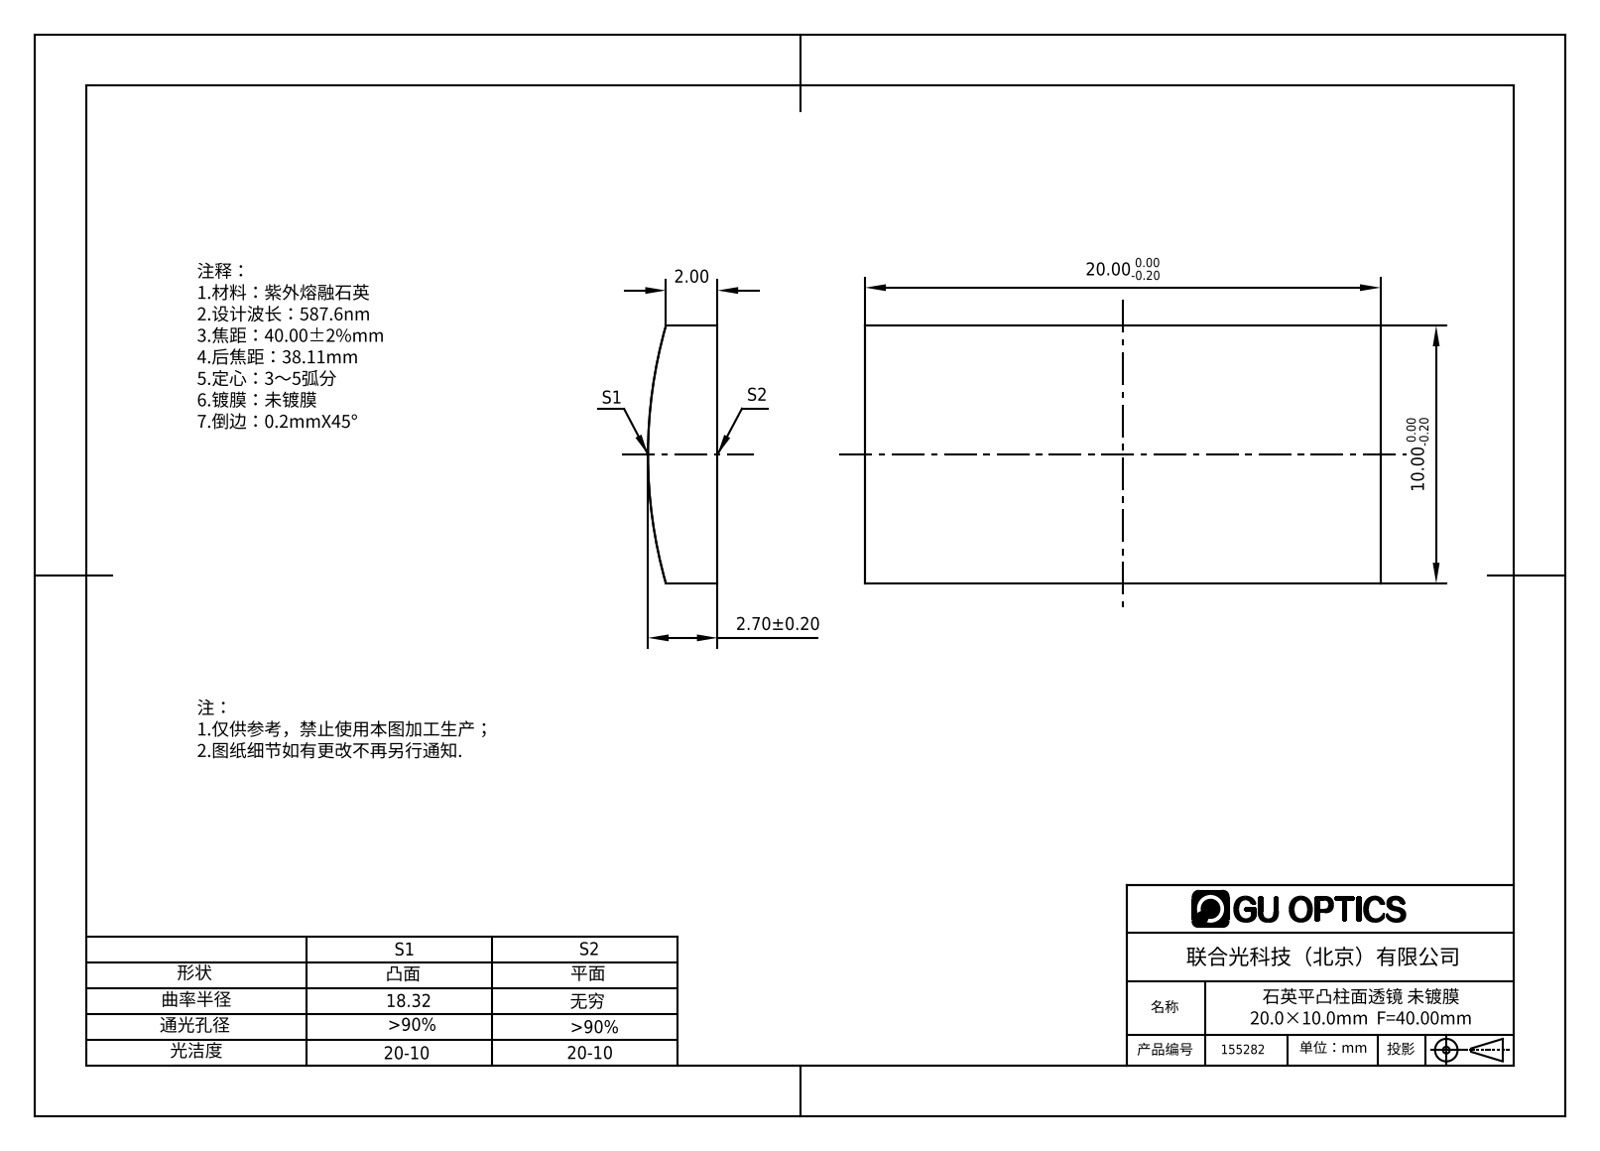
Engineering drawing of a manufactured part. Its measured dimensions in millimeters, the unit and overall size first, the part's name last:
Units: millimetres
Overall size (bounding box): 20 × 10 × 2.7
Partial cylindrical surfaces — rounded edges, fillets, slot ends (radius × count): R18.32 ×1
Main face-to-face distances: 10, 20
Volume: 494 mm³ · Surface area: 532 mm²
Bodies: 1 solid, 6 faces (5 planar, 1 cylindrical, 0 other)
Part name (STEP PRODUCT): 155282
STEP written by: SolidWorks 2016 (AUTOMOTIVE_DESIGN)
